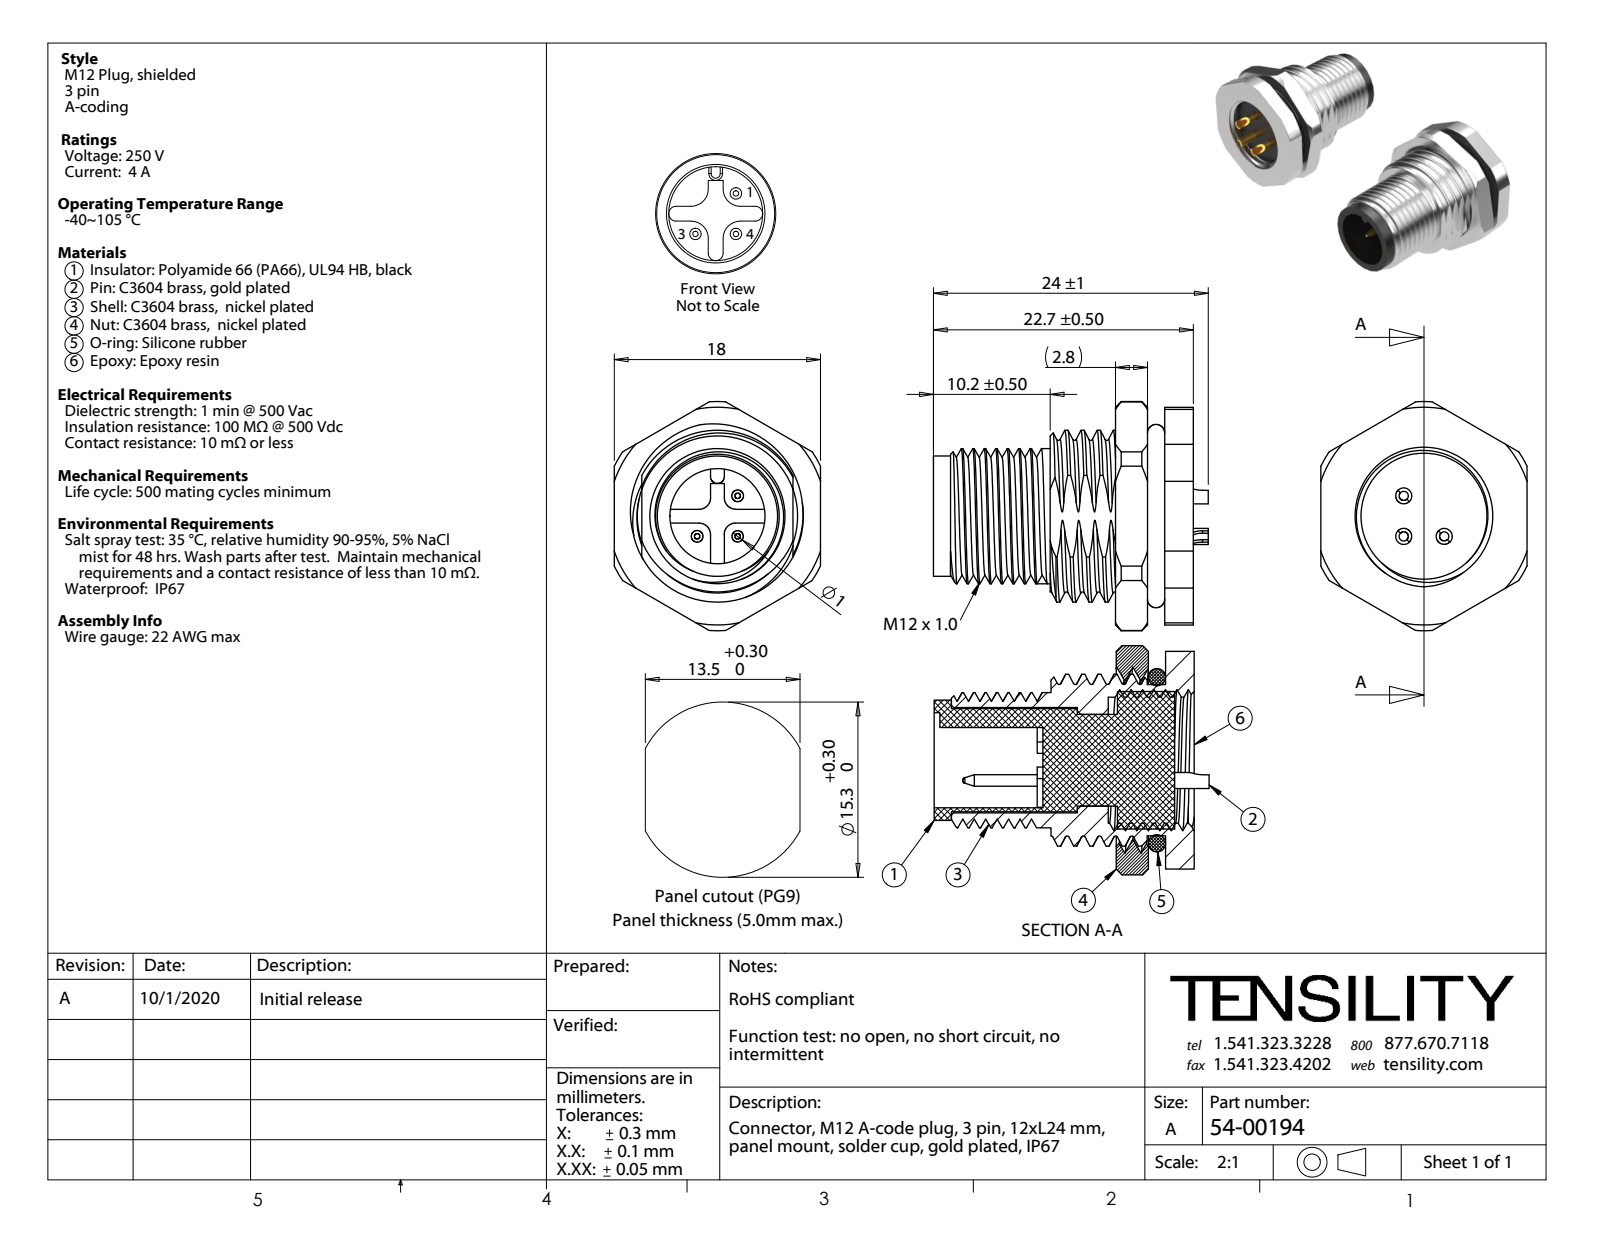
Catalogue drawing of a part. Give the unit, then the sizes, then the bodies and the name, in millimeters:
Units: millimetres
Overall size (bounding box): 24 × 20 × 18
Round holes (diameter × count): ⌀0.8 ×3, ⌀1 ×3, ⌀8 ×1, ⌀8.3 ×1, ⌀9.2 ×1, ⌀11 ×1, ⌀14 ×1
Round bosses / shafts (diameter × count): ⌀1.4 ×3, ⌀13.2 ×1, ⌀12 ×1, ⌀11.8 ×1, ⌀10.5 ×1, ⌀9 ×1
Partial cylindrical surfaces — rounded edges, fillets, slot ends (radius × count): R1 ×4, R1.96 ×3, R0.6 ×1, R7.5 ×1, R9.5 ×1, R10 ×1
Main face-to-face distances: 0.8, 5, 2.5, 1.5, 18, 2.3, 1.7, 2.7, 3.5, 4
Hole centre spacings: 2.5, 3.54, 5.01
Volume: 2 852 mm³ · Surface area: 5 079 mm²
Bodies: 7 solids, 327 faces (73 planar, 130 cylindrical, 124 other)
Part name (STEP PRODUCT): 54-00194-05; 54-00194; 54-00194-04; 54-00194-03 (+2 more)
STEP written by: SolidWorks 2015 (CONFIG_CONTROL_DESIGN)
